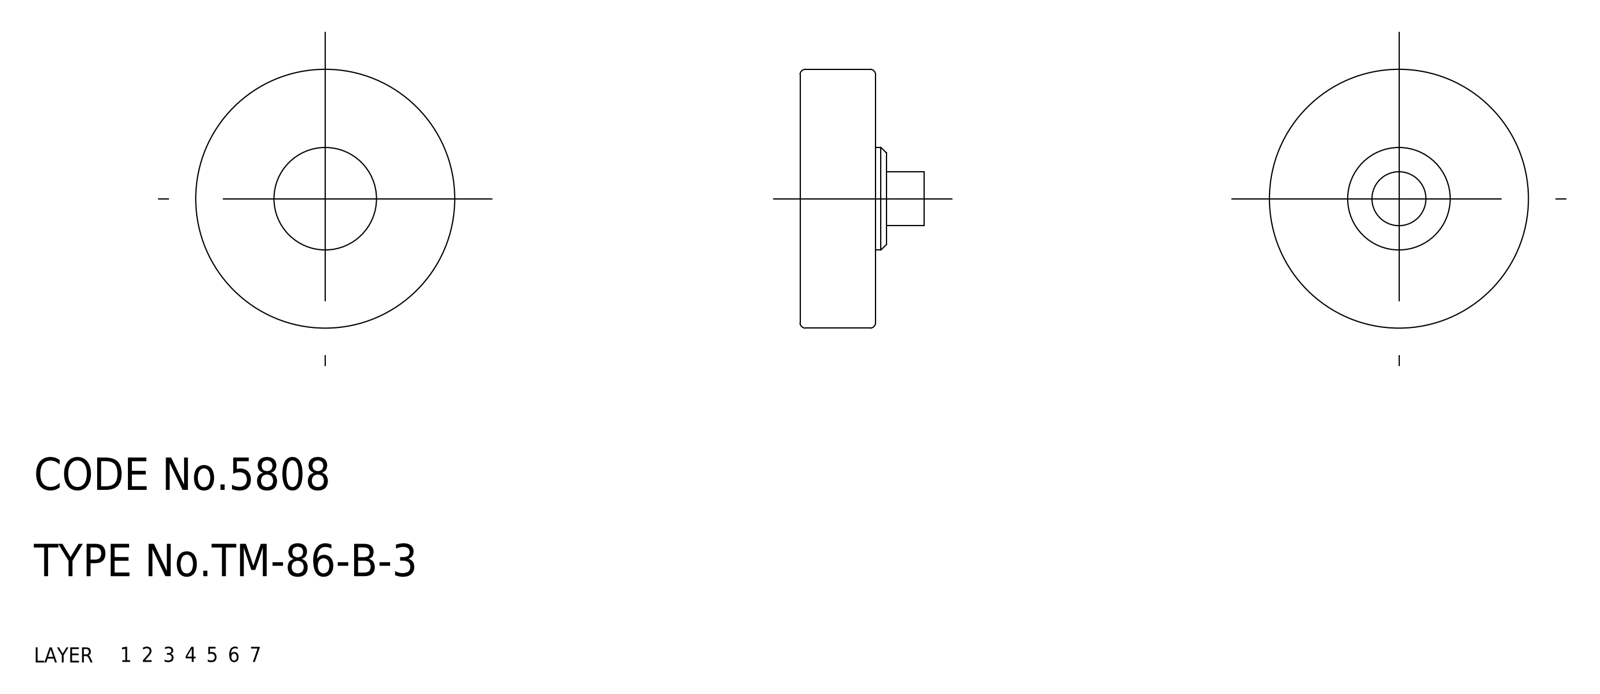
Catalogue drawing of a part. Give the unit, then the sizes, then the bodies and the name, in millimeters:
Units: millimetres
Overall size (bounding box): 24 × 24 × 11.5
Volume: 3 291 mm³ · Surface area: 1 988 mm²
Bodies: 1 solid, 30 faces (0 planar, 0 cylindrical, 30 other)
Part name (STEP PRODUCT): roller
STEP written by: CADfix (AUTOMOTIVE_DESIGN)
